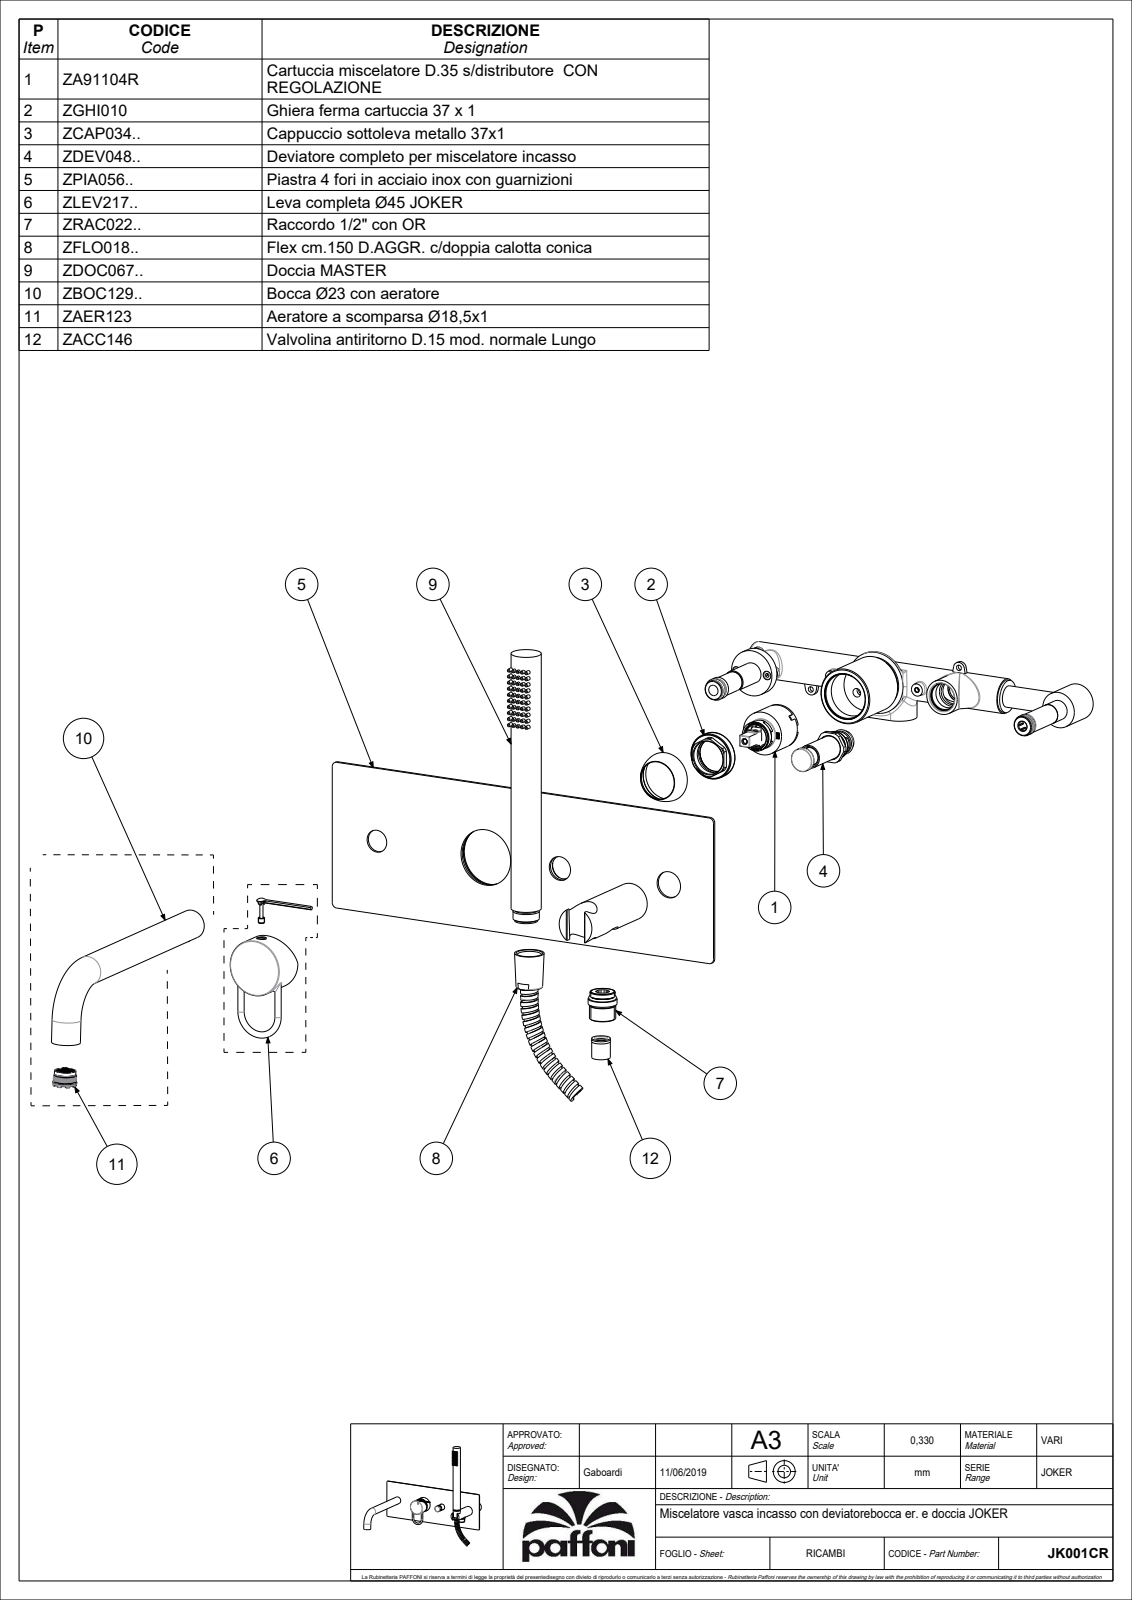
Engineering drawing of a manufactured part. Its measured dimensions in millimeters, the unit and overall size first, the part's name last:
Units: millimetres
Overall size (bounding box): 356.89 × 329.3 × 213.48
Round holes (diameter × count): ⌀3 ×1, ⌀4.2 ×1, ⌀5.5 ×1, ⌀30.6 ×1, ⌀36 ×1, ⌀37.5 ×1
Round bosses / shafts (diameter × count): ⌀5 ×3, ⌀23 ×2, ⌀20.9 ×2, ⌀45 ×1, ⌀44.8 ×1, ⌀30 ×1, ⌀24 ×1, ⌀18.7 ×1
Partial cylindrical surfaces — rounded edges, fillets, slot ends (radius × count): R4 ×4, R1.55 ×2, R11.5 ×1
Main face-to-face distances: 2, 49.1, 47.1, 120, 293, 173, 68, 86, 21, 19
Volume: 388 299 mm³ · Surface area: 165 493 mm²
Bodies: 22 solids, 407 faces (136 planar, 64 cylindrical, 207 other)
Part name (STEP PRODUCT): JK001CR
STEP written by: CREO PARAMETRIC BY PTC INC, 2020044 (CONFIG_CONTROL_DESIGN)
